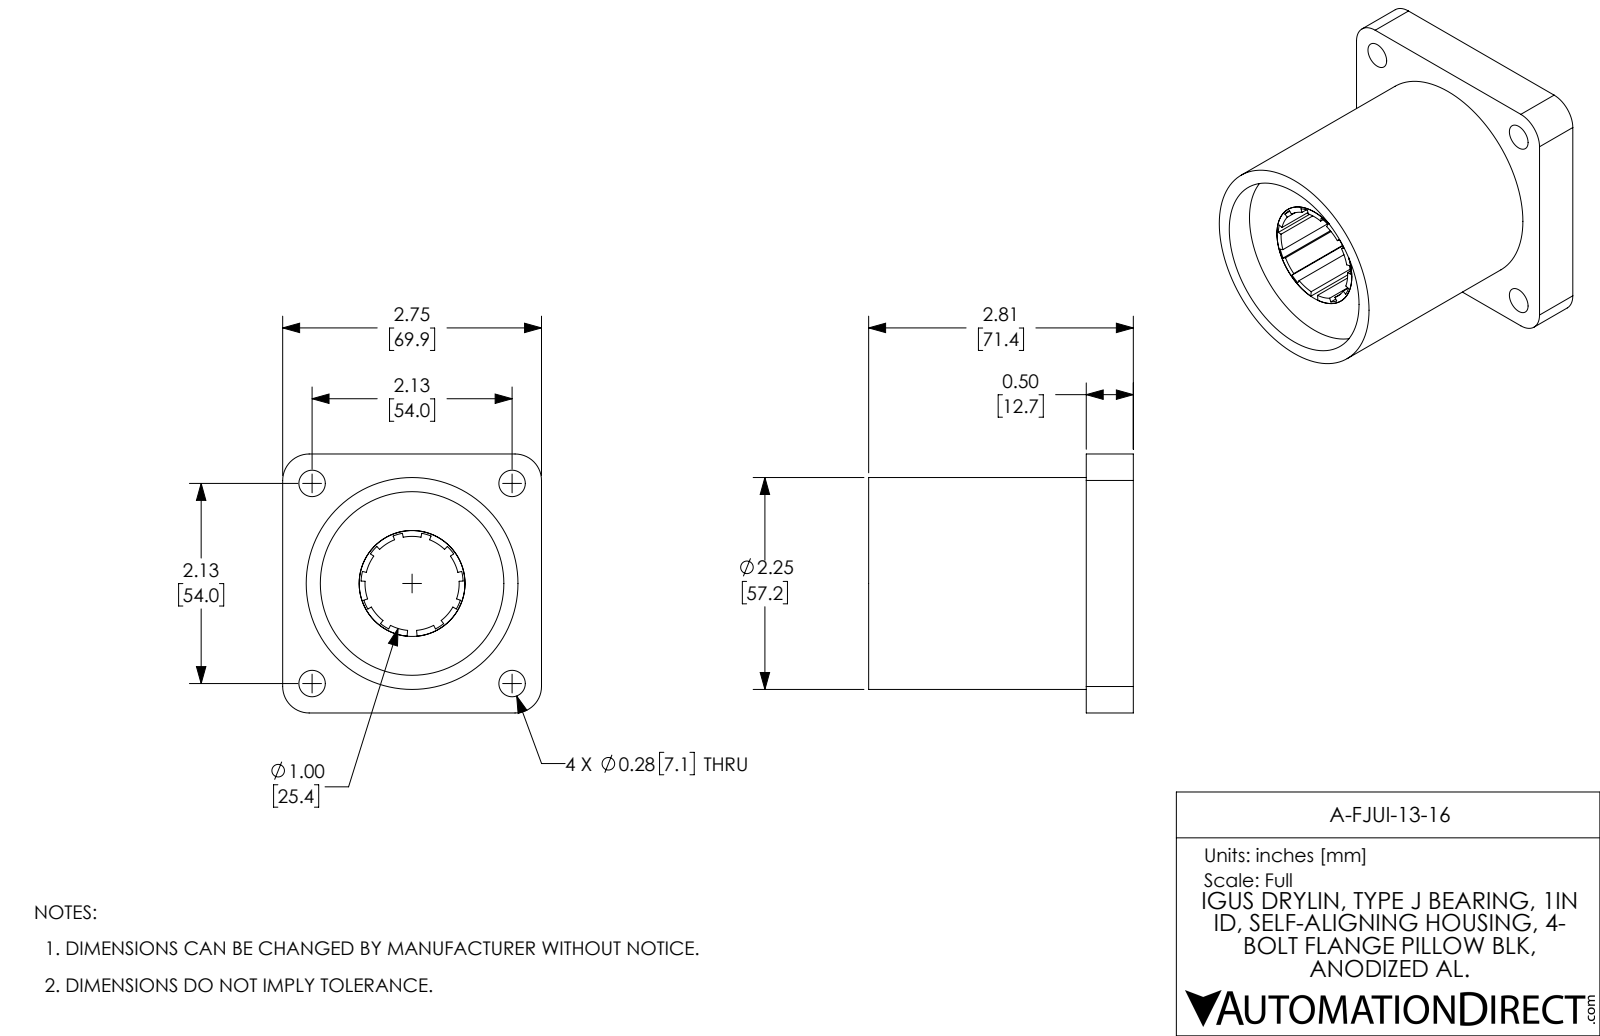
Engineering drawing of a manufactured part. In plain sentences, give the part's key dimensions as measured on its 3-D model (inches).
The part is named "A-FJUI-13-16". Its 3-D file was written by "SolidWorks 2017 (AUTOMOTIVE_DESIGN)". It is 2 solids with 135 faces: 76 planar, 59 cylindrical and 0 other. Overall it measures 2.812 by 2.75 by 2.75 inches. Its volume is 9.178 cubic inches and its surface area 64.64 square inches. Round holes: 4 of diameter 0.281, 1 of diameter 1.95. Round bosses or shafts: 1 of diameter 2.25, 1 of diameter 1.125, 1 of diameter 0.15. Partial cylindrical surfaces (rounded edges, fillets, slot ends): 4 of radius 0.281, 1 of radius 0.5, 1 of radius 0.543, 1 of radius 0.594. The main face-to-face distances are 0.5, 2.508, 0.304, 2.75, 2.008, 0.196, 2.205, 2.812, 2.312, 1.312. The hole center spacings are 1.503, 2.125, 3.006.
